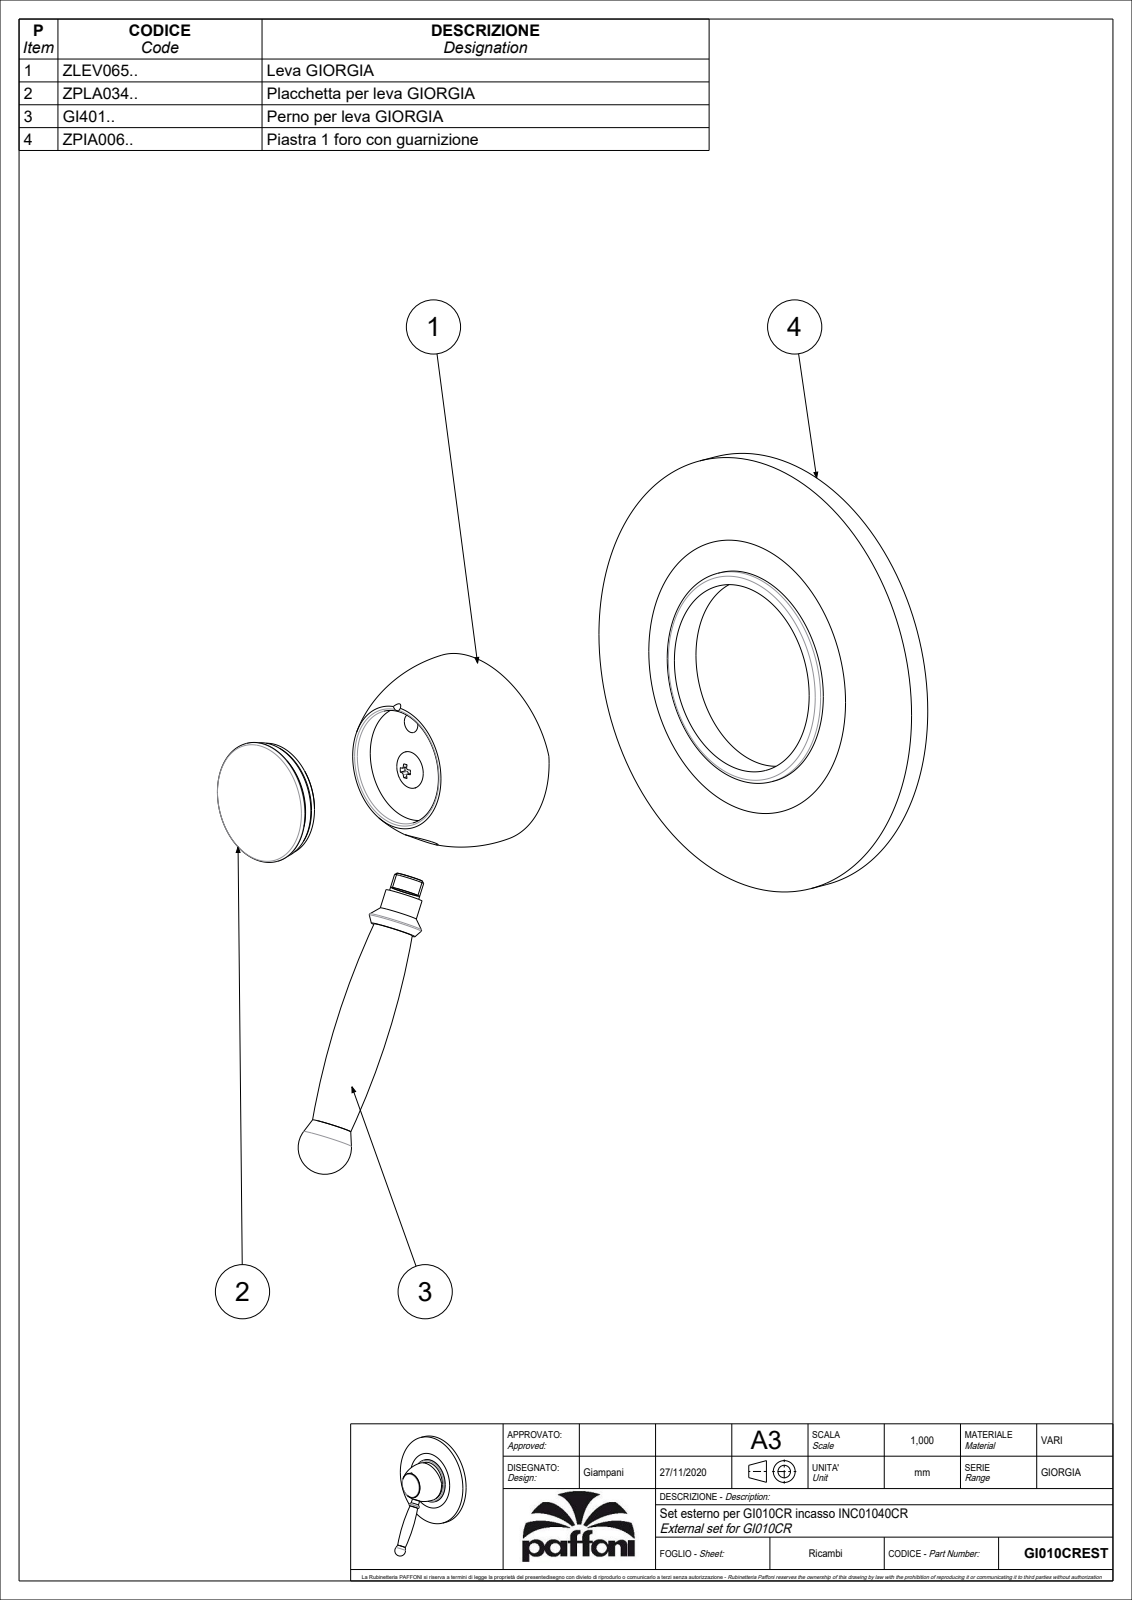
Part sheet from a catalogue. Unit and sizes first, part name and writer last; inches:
Units: inches
Overall size (bounding box): 5.892 × 4.567 × 2.81
Round holes (diameter × count): ⌀0.197 ×2, ⌀0.472 ×1, ⌀1.193 ×1, ⌀1.969 ×1, ⌀4.528 ×1
Round bosses / shafts (diameter × count): ⌀4.567 ×1, ⌀2.224 ×1, ⌀2.165 ×1, ⌀1.26 ×1, ⌀1.177 ×1, ⌀1.063 ×1, ⌀0.689 ×1, ⌀0.39 ×1
Partial cylindrical surfaces — rounded edges, fillets, slot ends (radius × count): R0.02 ×4, R0.079 ×1, R0.138 ×1, R0.959 ×1
Main face-to-face distances: 1.22, 0.315, 1.535, 0.906, 0.185, 1.406, 0.118, 0.13, 1.091, 0.197
Hole centre spacings: 0.063, 0.433, 0.496
Volume: 2.43 in³ · Surface area: 64.69 in²
Bodies: 2 solids, 211 faces (113 planar, 44 cylindrical, 54 other)
Part name (STEP PRODUCT): GI010CREST
STEP written by: CREO PARAMETRIC BY PTC INC, 2020044 (CONFIG_CONTROL_DESIGN)
